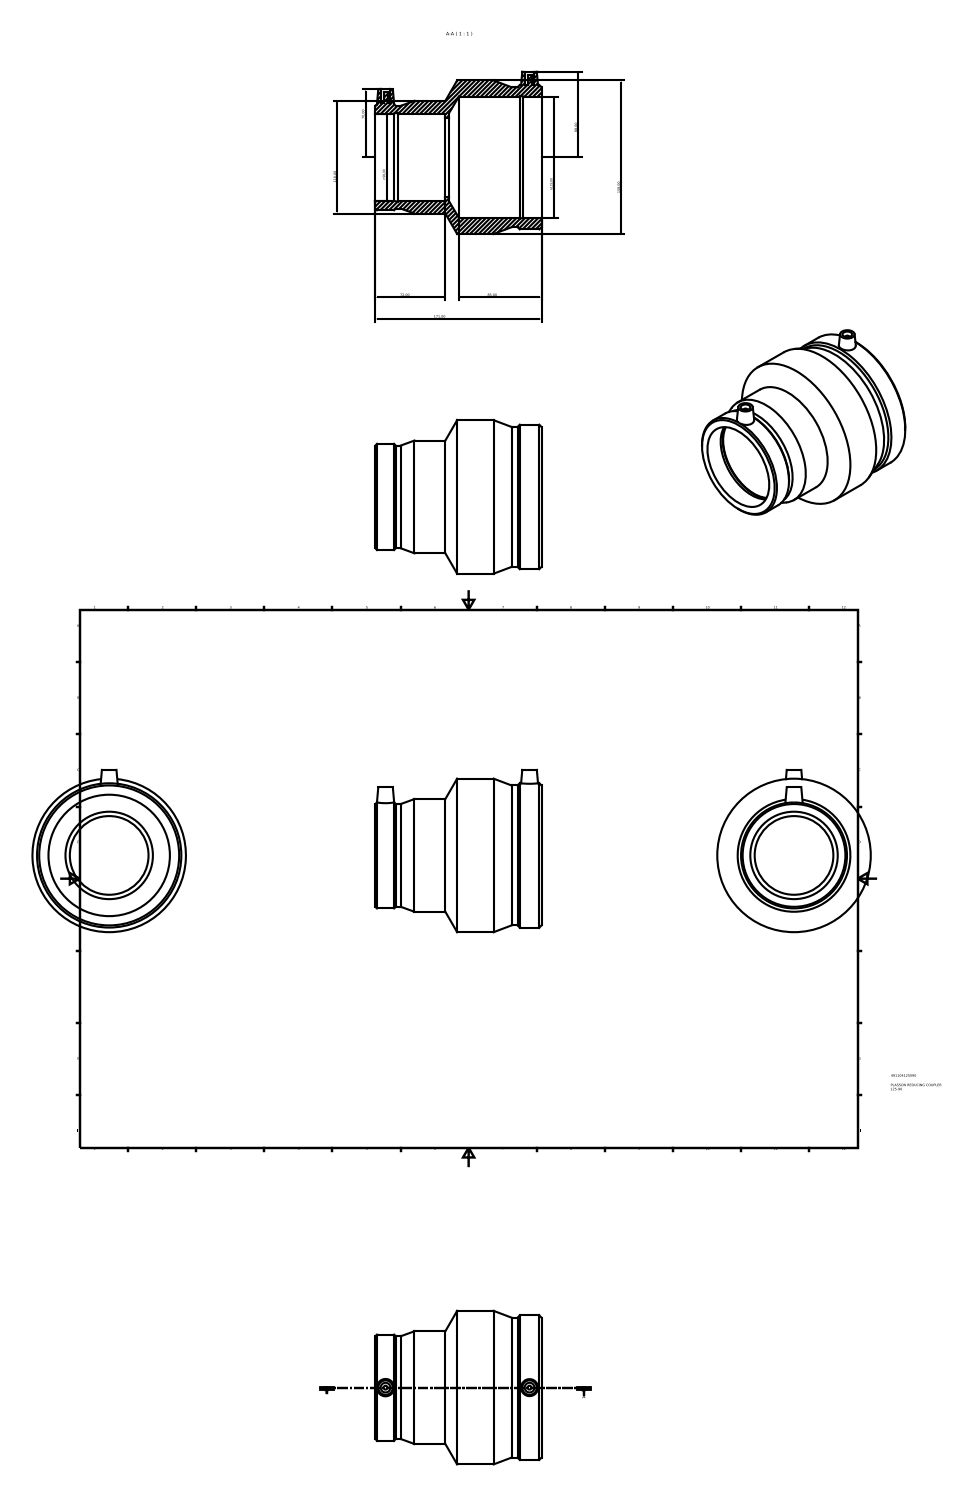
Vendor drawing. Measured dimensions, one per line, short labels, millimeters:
name: 491104125090
written by: Autodesk Inventor 2015 (AUTOMOTIVE_DESIGN)
unit: mm
bodies: 1 solid, 39 faces (12 planar, 15 cylindrical, 12 other)
size: 171 × 167 × 158
volume: 874 240 mm³; area: 153 262 mm²
holes: 2× ⌀10, 1× ⌀81, 1× ⌀90, 1× ⌀125
bosses: 2× ⌀4, 1× ⌀158, 1× ⌀148.52, 1× ⌀144.06, 1× ⌀116, 1× ⌀109.04, 1× ⌀105.77
face distances: 171, 75.6, 95.4, 72, 3.6, 99, 148.58, 76.58, 72.98, 22.42
hole spacings: 148.23
